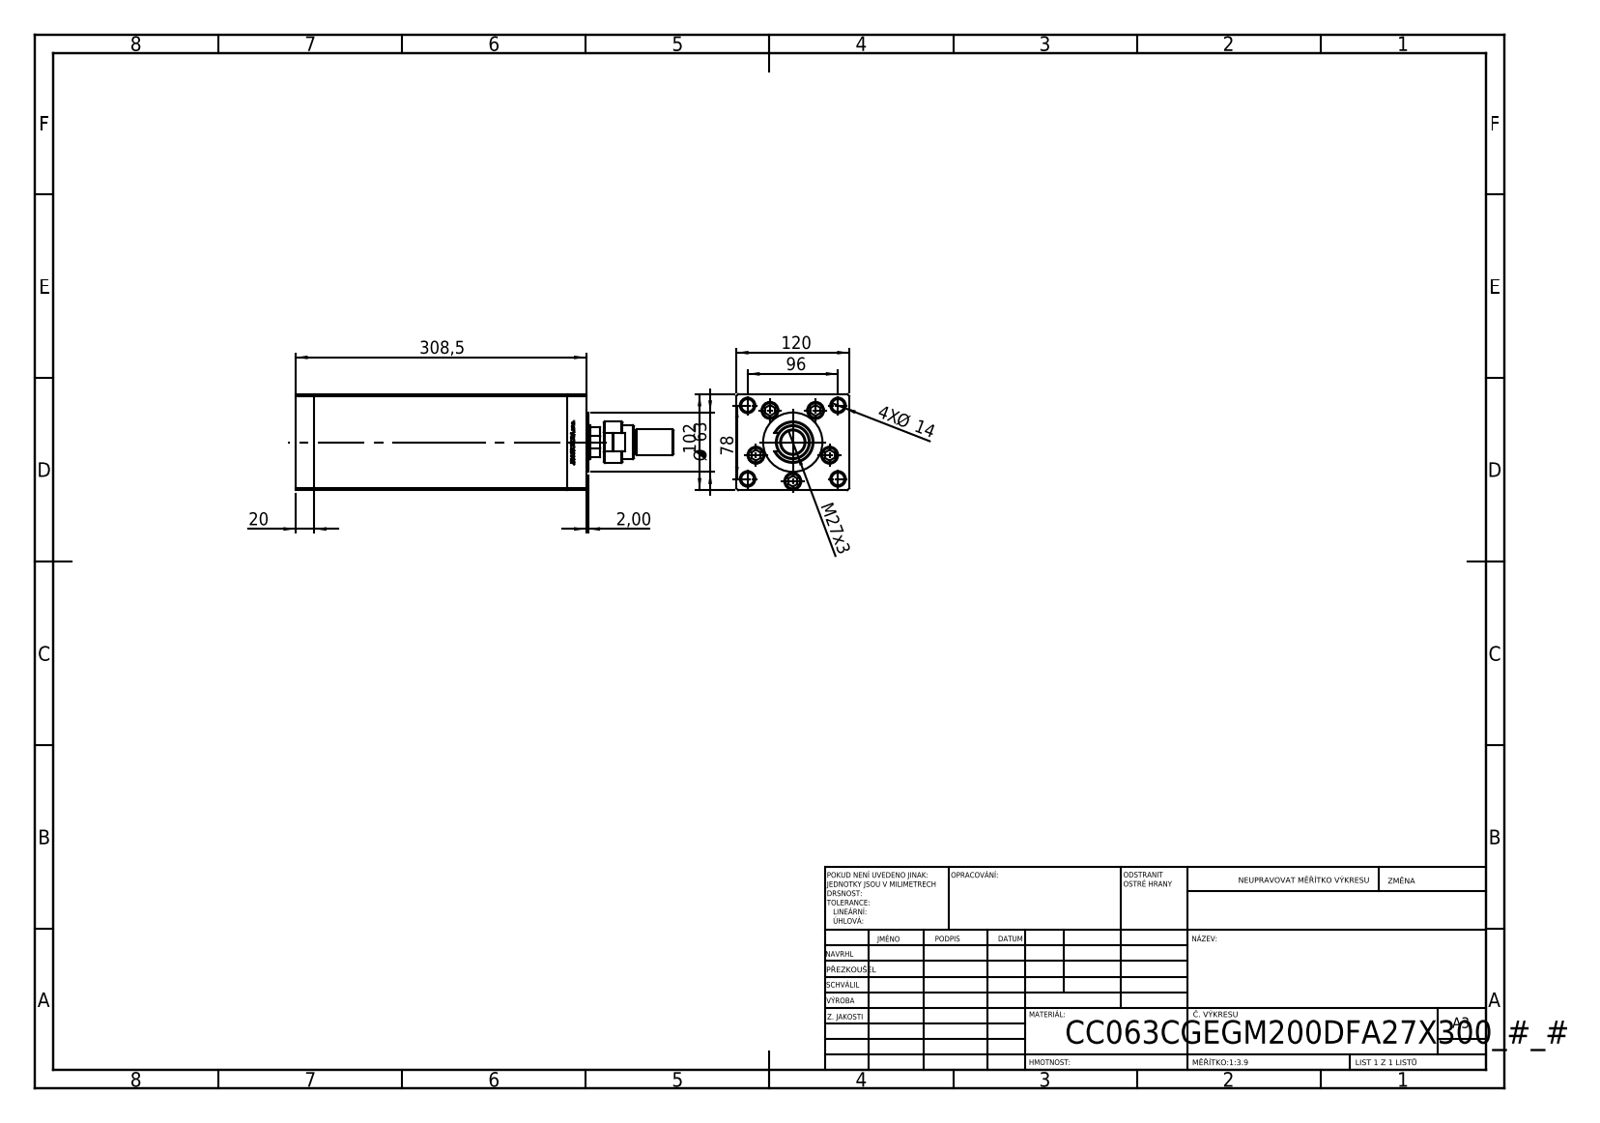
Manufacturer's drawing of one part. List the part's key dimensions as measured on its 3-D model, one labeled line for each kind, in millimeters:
Part name (STEP PRODUCT): V220C FRONT; V220C_VC_C; ALLEN BOLT; V220C BACK_C (+2 more)
STEP written by: SolidWorks 2019 (CONFIG_CONTROL_DESIGN)
Units: millimetres
Bodies: 14 solids, 1198 faces (554 planar, 170 cylindrical, 474 other)
Overall size (bounding box): 401.3 × 120 × 102
Volume: 3 185 000 mm³ · Surface area: 388 231 mm²
Round holes (diameter × count): ⌀13.5 ×9, ⌀18 ×5, ⌀12 ×4, ⌀16.5 ×4, ⌀17 ×1, ⌀25.5 ×1
Round bosses / shafts (diameter × count): ⌀8 ×5, ⌀17 ×4, ⌀63 ×1, ⌀44 ×1, ⌀36 ×1, ⌀27 ×1, ⌀25 ×1
Partial cylindrical surfaces — rounded edges, fillets, slot ends (radius × count): R0.93 ×2, R9.5 ×1, R15 ×1, R17.5 ×1
Main face-to-face distances: 120, 102, 20, 268.5, 288.5, 34.25, 308.5, 274.25, 254.25, 14.25
Hole centre spacings: 41.5, 61.85, 24.39, 26.69, 47.92, 48.07, 49.84, 53.57
